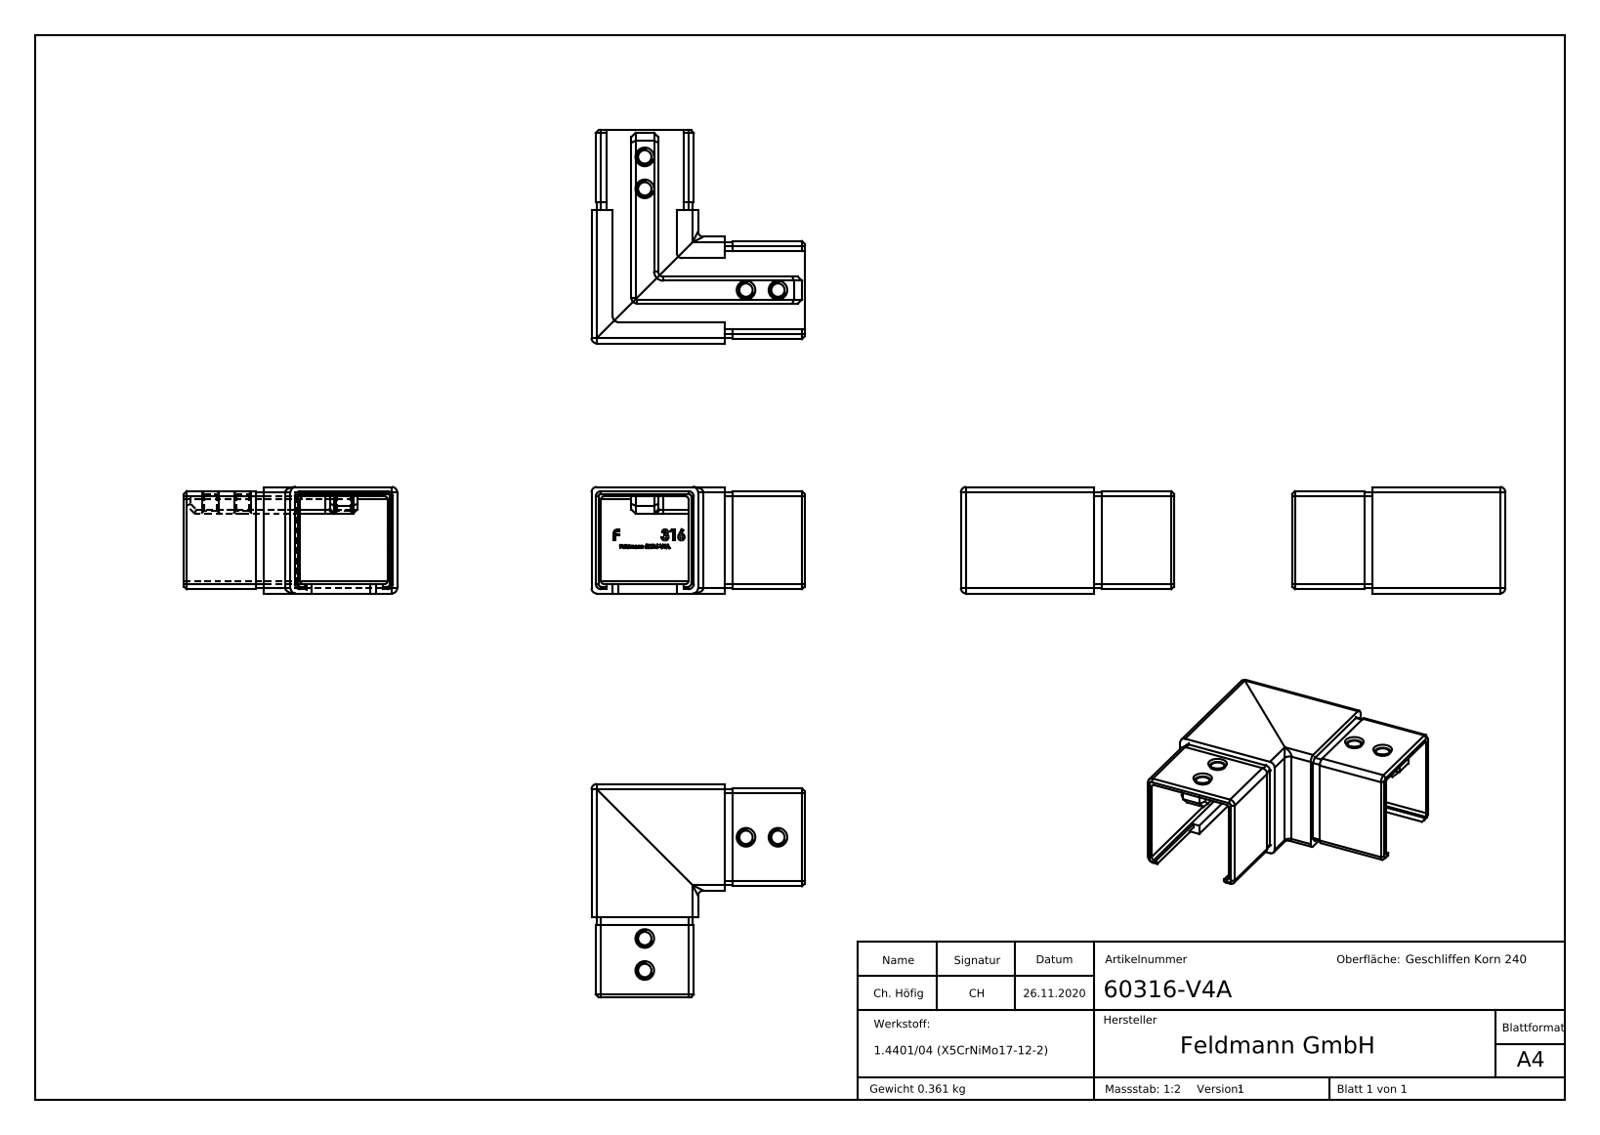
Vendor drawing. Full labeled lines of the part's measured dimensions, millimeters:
Part name (STEP PRODUCT): 60316-V4A
STEP written by: SolidWorks 2018 (CONFIG_CONTROL_DESIGN)
Units: millimetres
Bodies: 1 solid, 452 faces (262 planar, 46 cylindrical, 144 other)
Overall size (bounding box): 80 × 80 × 40
Volume: 45 176 mm³ · Surface area: 30 407 mm²
Round holes (diameter × count): ⌀5 ×4
Partial cylindrical surfaces — rounded edges, fillets, slot ends (radius × count): R2 ×22, R1 ×8, R1.5 ×8
Main face-to-face distances: 3.6, 2, 36.4, 34.8, 1.6, 32.8, 38.4, 36.8, 10, 25
Hole centre spacings: 12, 62.8, 53.74, 70.71
